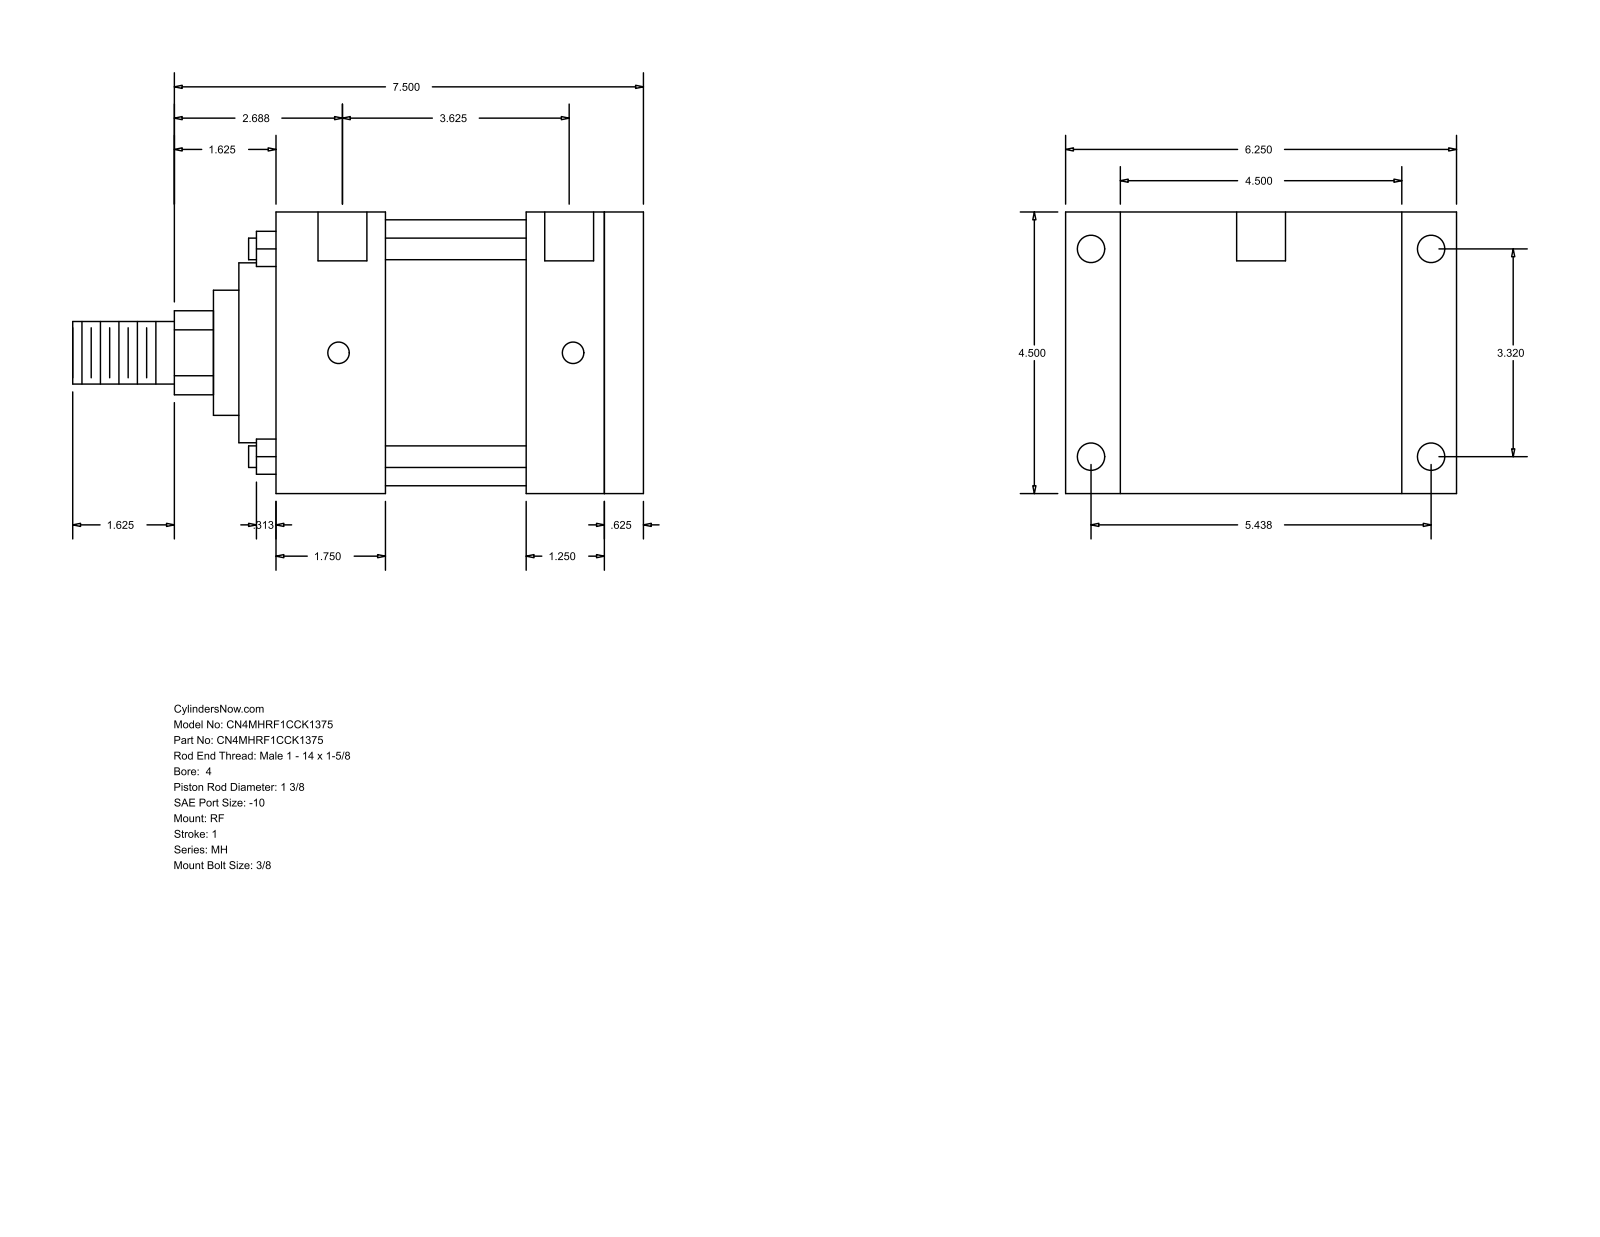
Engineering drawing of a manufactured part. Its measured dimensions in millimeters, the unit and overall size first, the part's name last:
Units: millimetres
Overall size (bounding box): 231.78 × 158.75 × 114.3
Round holes (diameter × count): ⌀8.73 ×4, ⌀11.13 ×4, ⌀19.84 ×2
Round bosses / shafts (diameter × count): ⌀8.76 ×4, ⌀107.95 ×1, ⌀73.03 ×1, ⌀50.8 ×1, ⌀34.92 ×1, ⌀25.4 ×1
Partial cylindrical surfaces — rounded edges, fillets, slot ends (radius × count): R17.06 ×1
Main face-to-face distances: 114.3, 149.23, 15.88, 133.35, 44.45, 88.9, 104.78, 101.61, 57.16, 31.74
Hole centre spacings: 1.59, 84.32, 93.67, 95.26, 138.12, 161.82, 92.08
Bodies: 0 solids, 94 faces (65 planar, 29 cylindrical, 0 other)
Part name (STEP PRODUCT): MH_RF__0400_1.375
STEP written by: GSSL Pune (CONFIG_CONTROL_DESIGN)
